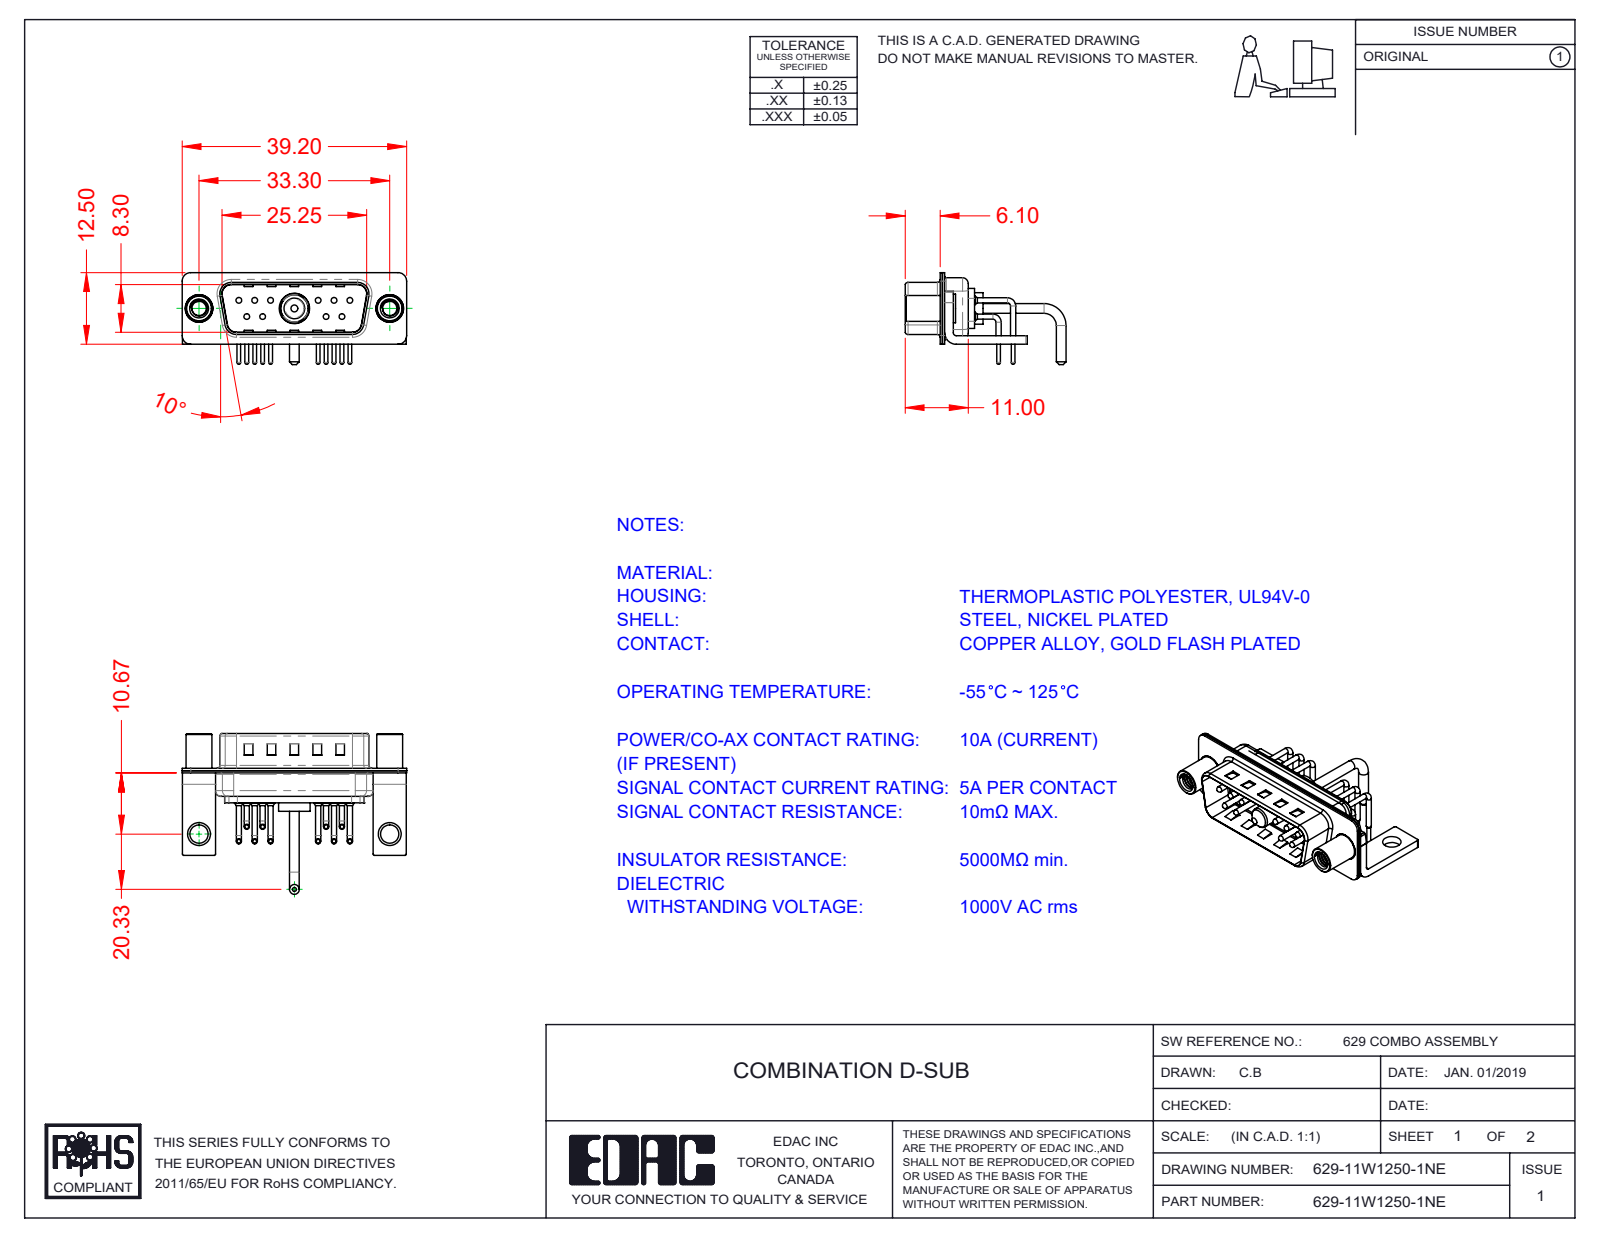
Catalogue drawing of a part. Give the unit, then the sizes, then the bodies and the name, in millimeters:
Units: millimetres
Overall size (bounding box): 39.2 × 28.08 × 16.05
Round holes (diameter × count): ⌀0.75 ×10, ⌀1.6 ×10, ⌀2 ×10, ⌀2.5 ×2, ⌀3.2 ×2, ⌀4 ×2, ⌀4.8 ×2, ⌀4.85 ×1, ⌀5.3 ×1
Round bosses / shafts (diameter × count): ⌀0.9 ×20, ⌀1.5 ×10, ⌀1 ×10, ⌀0.65 ×10, ⌀5 ×2, ⌀4.9 ×2, ⌀4.5 ×2, ⌀1.7 ×2
Partial cylindrical surfaces — rounded edges, fillets, slot ends (radius × count): R0.25 ×16, R1.5 ×16, R2 ×13, R1.01 ×10, R0.5 ×9, R1.6 ×8, R1 ×7, R0.6 ×4
Main face-to-face distances: 0.4, 0.8, 1.5, 9.5, 9.1, 8.7, 9.9, 0.6, 1.9, 5.2
Hole centre spacings: 3.16, 2.77, 13.85, 11.08, 16.62, 5.03, 5.04, 5.54
Volume: 2 405 mm³ · Surface area: 6 145 mm²
Bodies: 19 solids, 1594 faces (820 planar, 590 cylindrical, 184 other)
Part name (STEP PRODUCT): 629Combo Stabilizer Bracket; 629Combo Contact Row 1; Power Pin_Ext 10A RA; 629Combo Housing_11W1 (+5 more)
STEP written by: SolidWorks 2020 (CONFIG_CONTROL_DESIGN)
